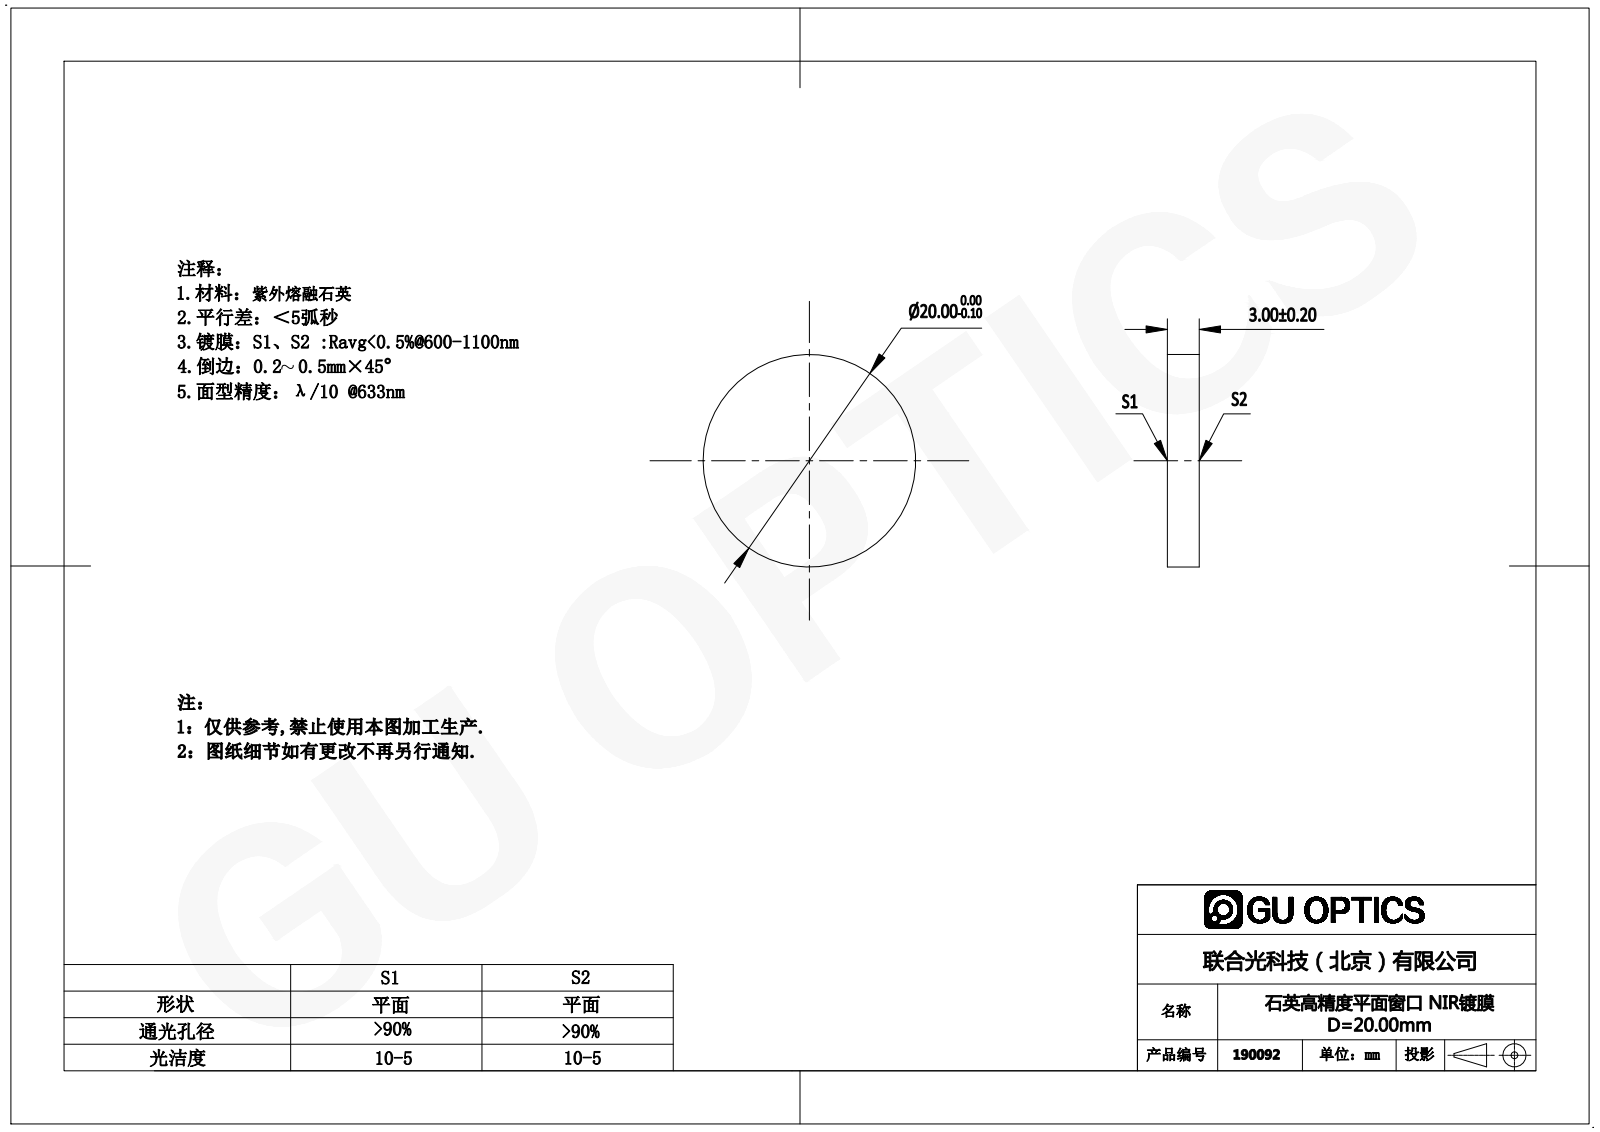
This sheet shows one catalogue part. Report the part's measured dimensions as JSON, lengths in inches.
{"part_name": "190059", "step_written_by": "SolidWorks 2016 (AUTOMOTIVE_DESIGN)", "units": "inches", "bodies": {"solids": 1, "faces": 4, "planar": 2, "cylindrical": 2, "other": 0}, "overall_size": [0.787, 0.787, 0.118], "volume_in3": 0.057, "surface_area_in2": 1.27, "round_bosses_or_shafts": [[0.787, 1]], "face_to_face_distances": [0.118]}
